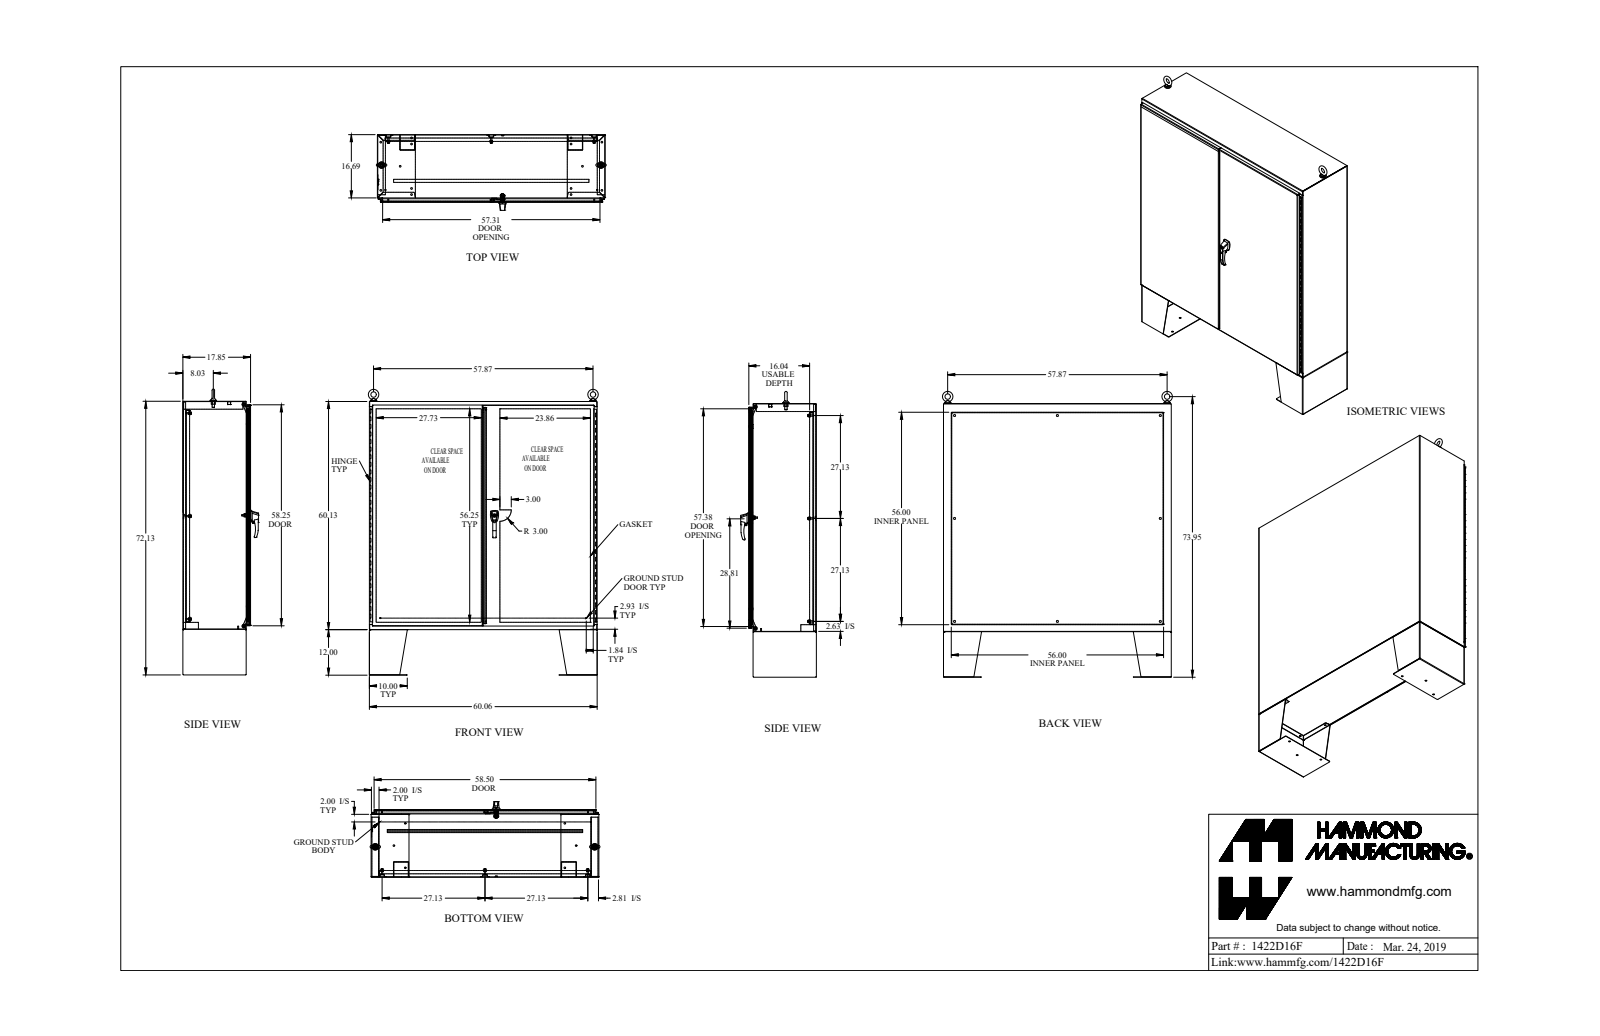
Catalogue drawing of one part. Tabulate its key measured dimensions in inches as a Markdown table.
| quantity | value |
| --- | --- |
| part name | 1422D16F_Default |
| STEP written by | SolidWorks 2019 (CONFIG_CONTROL_DESIGN) |
| units | inches |
| bodies | 90 solids, 2769 faces (1280 planar, 1242 cylindrical, 247 other) |
| overall size | 75.778 × 61.121 × 19.963 |
| volume | 1 817 in³ |
| surface area | 36 164 in² |
| round holes (diameter × count) | 0.304 × 20, 0.437 × 14, 0.307 × 9, 0.563 × 8, 0.445 × 6, 0.11 × 2, 0.25 × 2, 0.257 × 2, 0.28 × 2, 0.281 × 2, 0.313 × 2, 0.39 × 2 |
| round bosses / shafts (diameter × count) | 1 × 10, 0.65 × 8, 0.375 × 8, 0.33 × 8, 0.281 × 6, 0.25 × 4, 1.75 × 2, 1.5 × 2 |
| partial cylindrical surfaces (radius × count) | 0.048 × 32, 0.143 × 32, 0.125 × 22, 0.018 × 16, 0.06 × 14, 0.116 × 12, 0.05 × 8, 0.185 × 8 |
| main face-to-face distances | 0.095, 0.095, 17.658, 17.753, 17.753, 17.848, 0.125, 16.066, 15.971, 1.687 |
| hole center spacings | 6, 58.7, 12, 59.613, 18, 61.104, 24, 63.132 |
